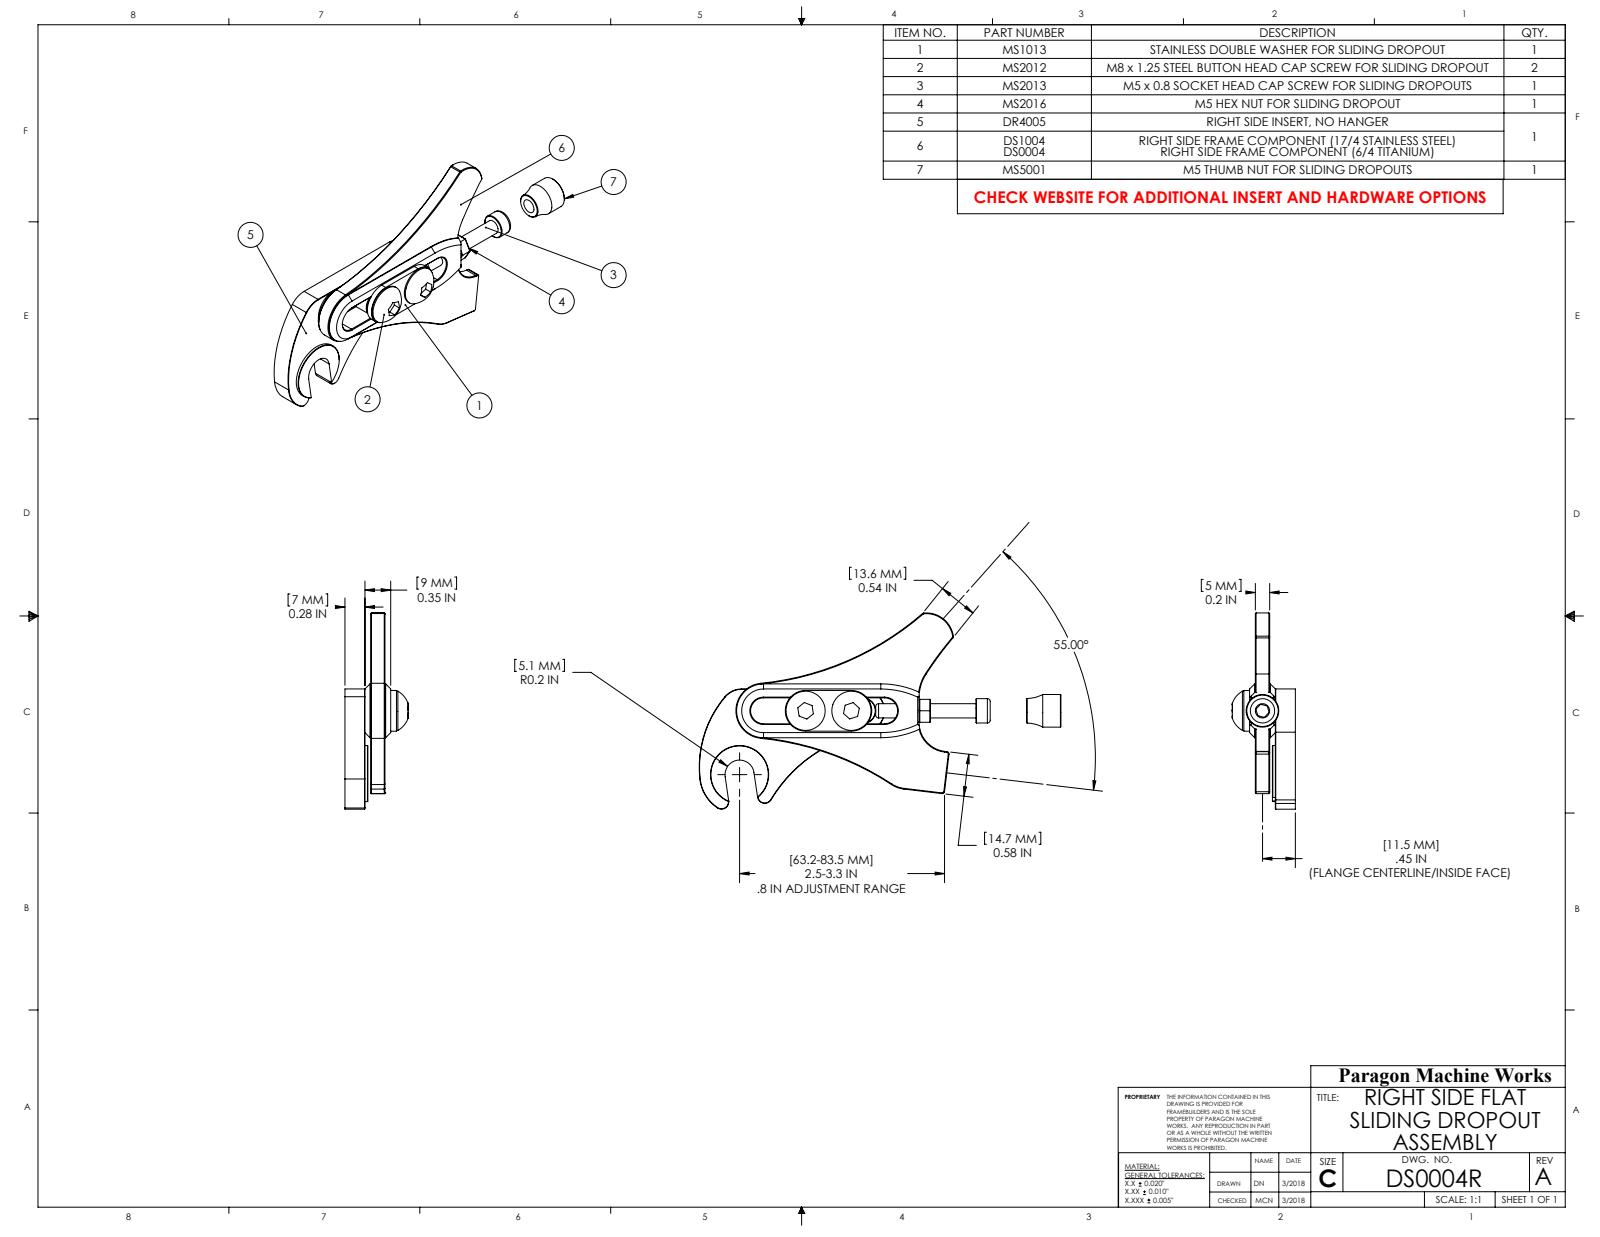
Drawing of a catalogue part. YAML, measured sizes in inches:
part_name: "DS0004R; PA0020; DR4005; MS5001 (+4 more)"
step_written_by: "SolidWorks 2012 (AUTOMOTIVE_DESIGN)"
units: inches
bodies: {solids: 8, faces: 255, planar: 86, cylindrical: 84, other: 85}
overall_size: [4.974, 2.698, 0.869]
volume: 1.744
surface_area: 25.61
round_holes:
  - {diameter: 0.312, count: 2}
  - {diameter: 0.327, count: 2}
  - {diameter: 0.197, count: 1}
  - {diameter: 0.335, count: 1}
round_bosses_or_shafts:
  - {diameter: 0.539, count: 2}
  - {diameter: 0.315, count: 2}
  - {diameter: 0.8, count: 1}
  - {diameter: 0.449, count: 1}
partial_cylinders:
  - {radius: 0.01, count: 12}
  - {radius: 0.03, count: 4}
  - {radius: 0.178, count: 4}
  - {radius: 0.1, count: 2}
  - {radius: 0.28, count: 2}
  - {radius: 0.3, count: 2}
  - {radius: 0.4, count: 2}
  - {radius: 1.27, count: 2}
face_to_face_distances: [0.079, 0.276, 0.275, 0.197, 0.354, 0.551, 0.354, 0.63, 0.356, 0.157]
hole_center_spacings: [0.63]
